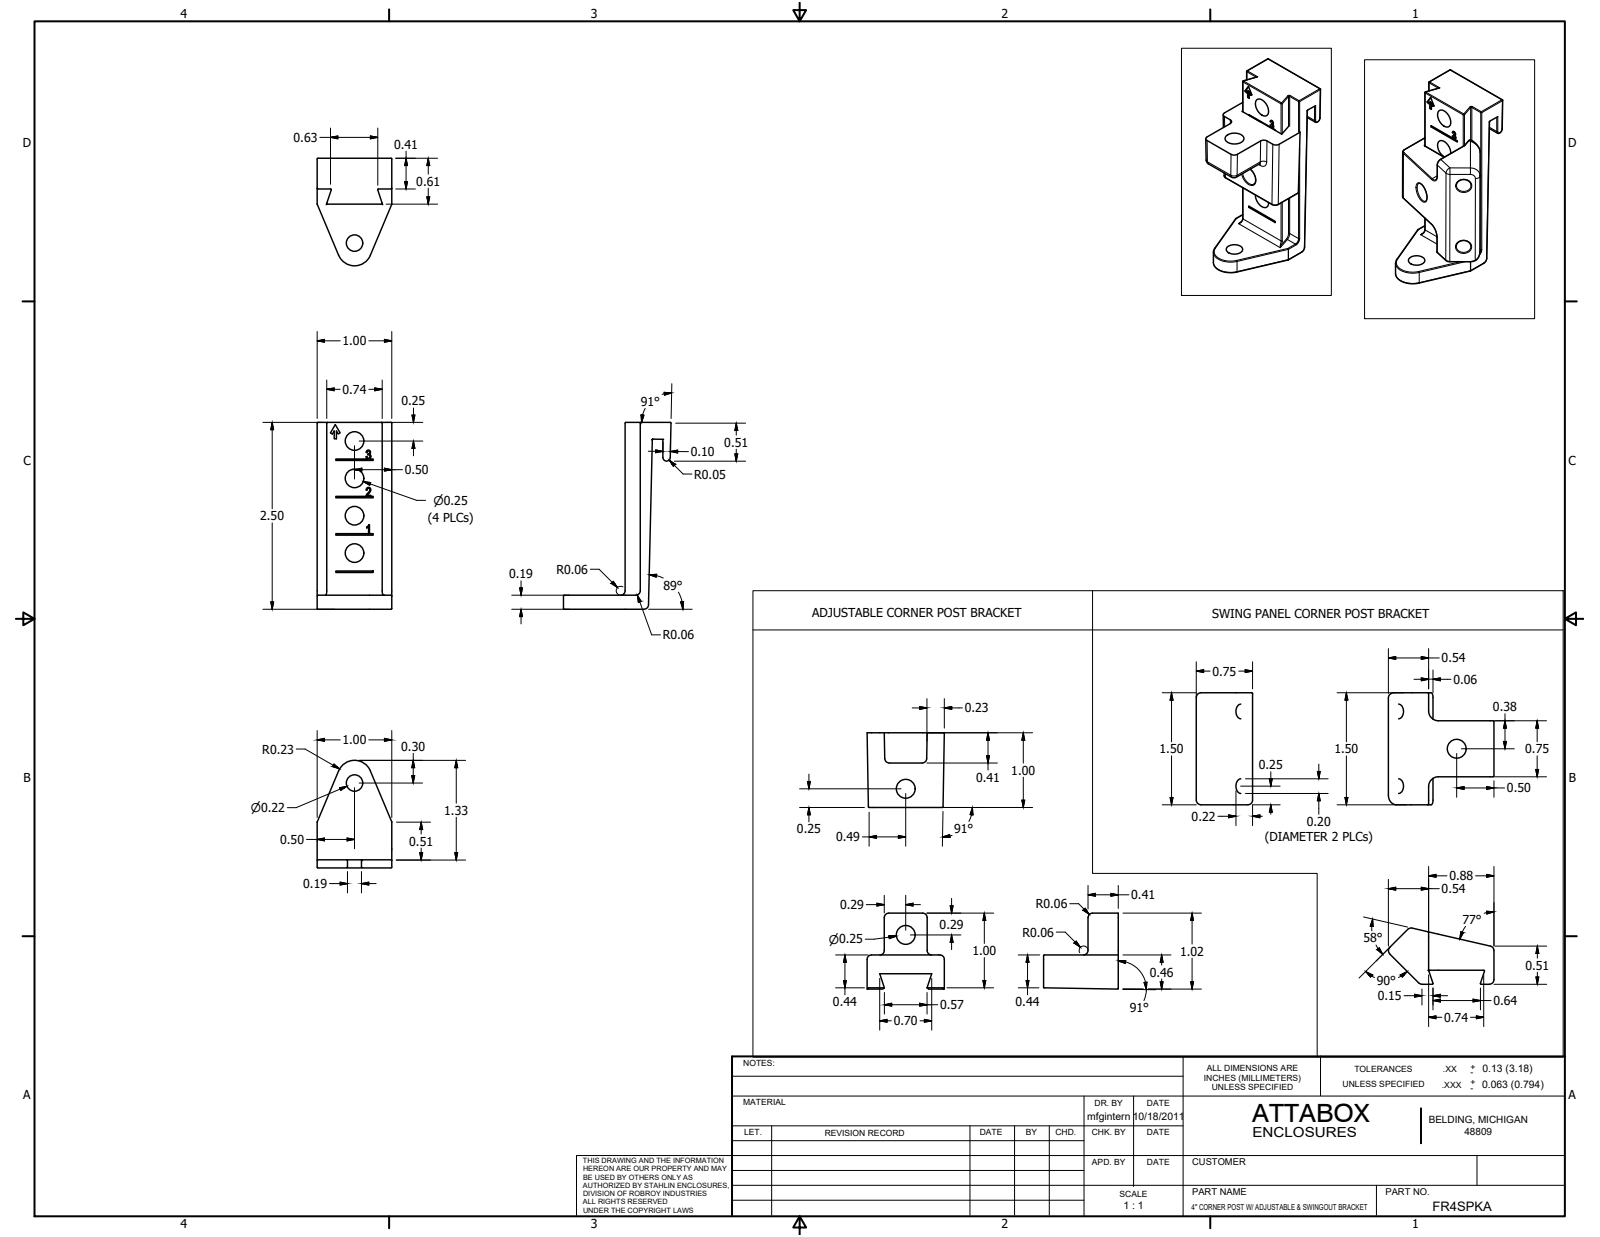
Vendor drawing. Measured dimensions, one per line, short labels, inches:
name: FR4SPKA
written by: SolidWorks 2019 (AUTOMOTIVE_DESIGN)
unit: in
bodies: 28 solids, 1192 faces (492 planar, 378 cylindrical, 322 other)
size: 8.557 × 8.556 × 2.728
volume: 5.96 in³; area: 86.12 in²
holes: 18× ⌀0.25, 6× ⌀0.253, 4× ⌀0.217, 4× ⌀0.22, 2× ⌀0.156, 2× ⌀0.312, 2× ⌀0.35
bosses: 10× ⌀0.19, 6× ⌀0.373, 4× ⌀0.433, 4× ⌀0.315, 2× ⌀0.246
rounds: 210× R0.01, 40× R0.06, 10× R0.063, 8× R0.025, 8× R0.062, 8× R0.13, 4× R0.049, 4× R0.19
face distances: 9.881, 0.08, 2.502, 0.188, 4.644, 5.643, 2.314, 0.203, 10.084, 0.1
hole spacings: 0.5, 1, 1.5, 0.872, 6.25, 6.252, 6.25, 6.913
